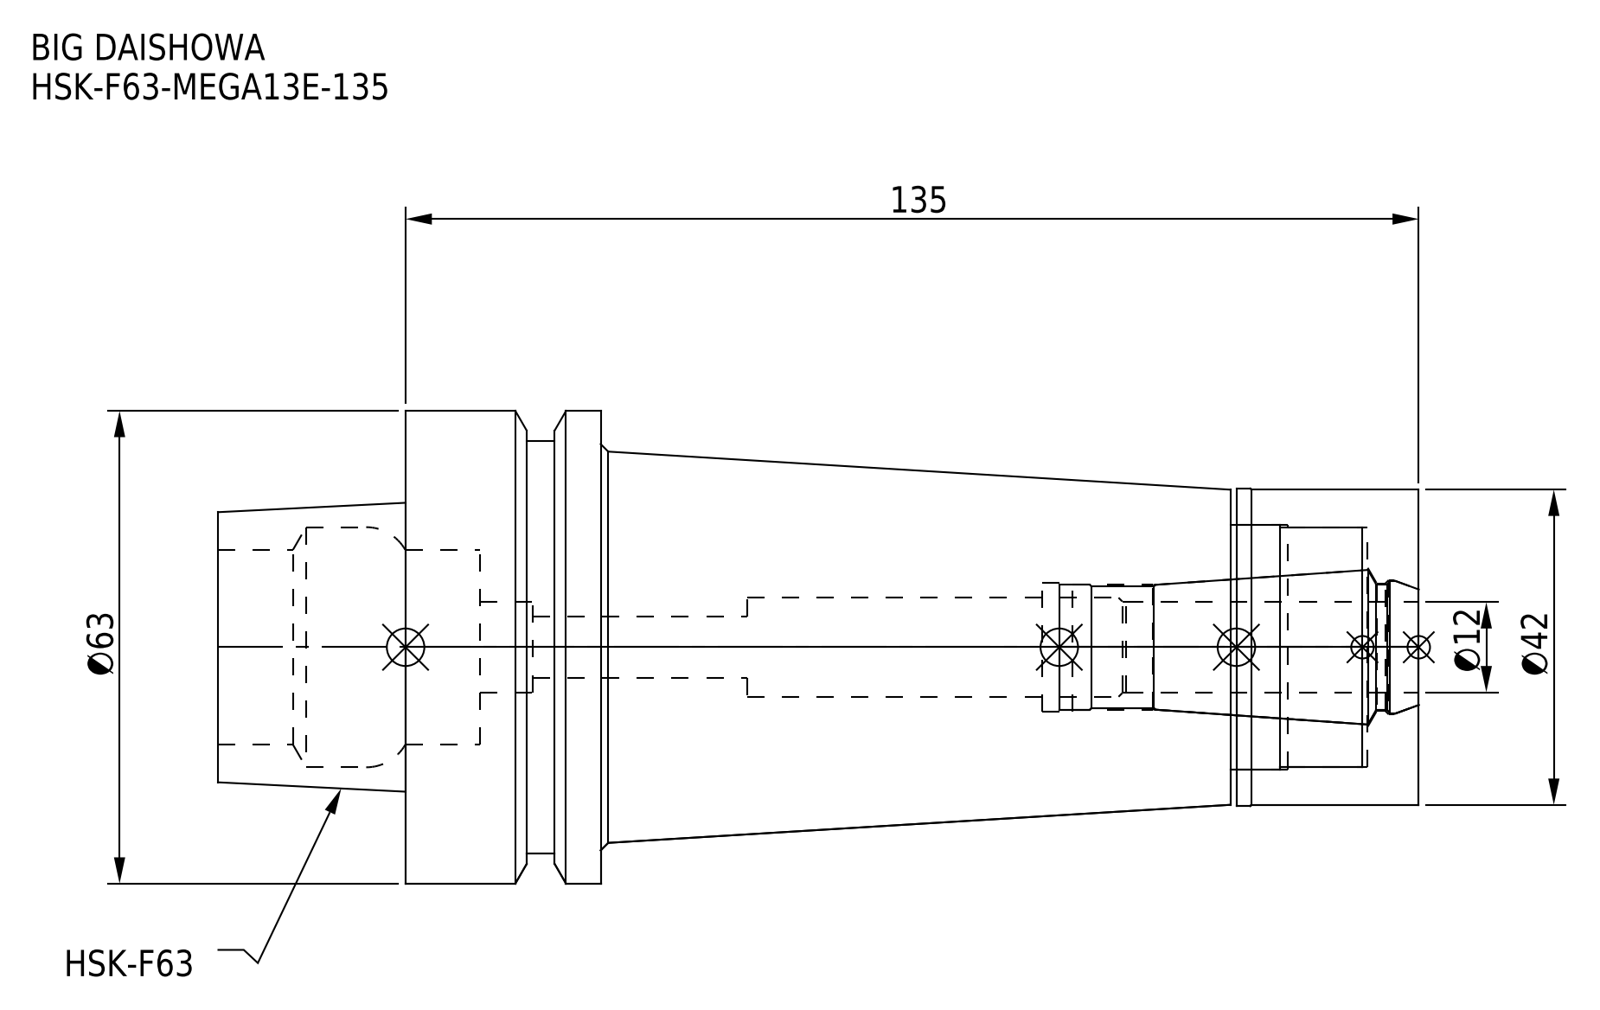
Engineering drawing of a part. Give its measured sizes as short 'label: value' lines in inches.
name: MEN13_1.stp; HSK-F63-MEGA13E-135-120.stp; DXF_TEMP_ASSY_ASM_4_ASM.stp; HSK-F63-MEGA13E-135_1.stp (+3 more)
written by: SolidWorks 2019 (CONFIG_CONTROL_DESIGN)
unit: in
bodies: 2 solids, 81 faces (17 planar, 40 cylindrical, 24 other)
size: 6.299 × 2.48 × 2.48
volume: 14.85 in³; area: 68.83 in²
holes: 1× ⌀0.325, 1× ⌀0.472, 1× ⌀0.524, 1× ⌀0.654, 1× ⌀0.669, 1× ⌀0.677, 1× ⌀0.705, 1× ⌀1.024, 1× ⌀1.26, 1× ⌀1.28
bosses: 1× ⌀2.48, 1× ⌀2.165, 1× ⌀1.665, 1× ⌀1.654
face distances: 5.315, 4.291, 1.024, 0.988, 0.957, 3.335, 4.358, 0.031, 3.303, 4.327
